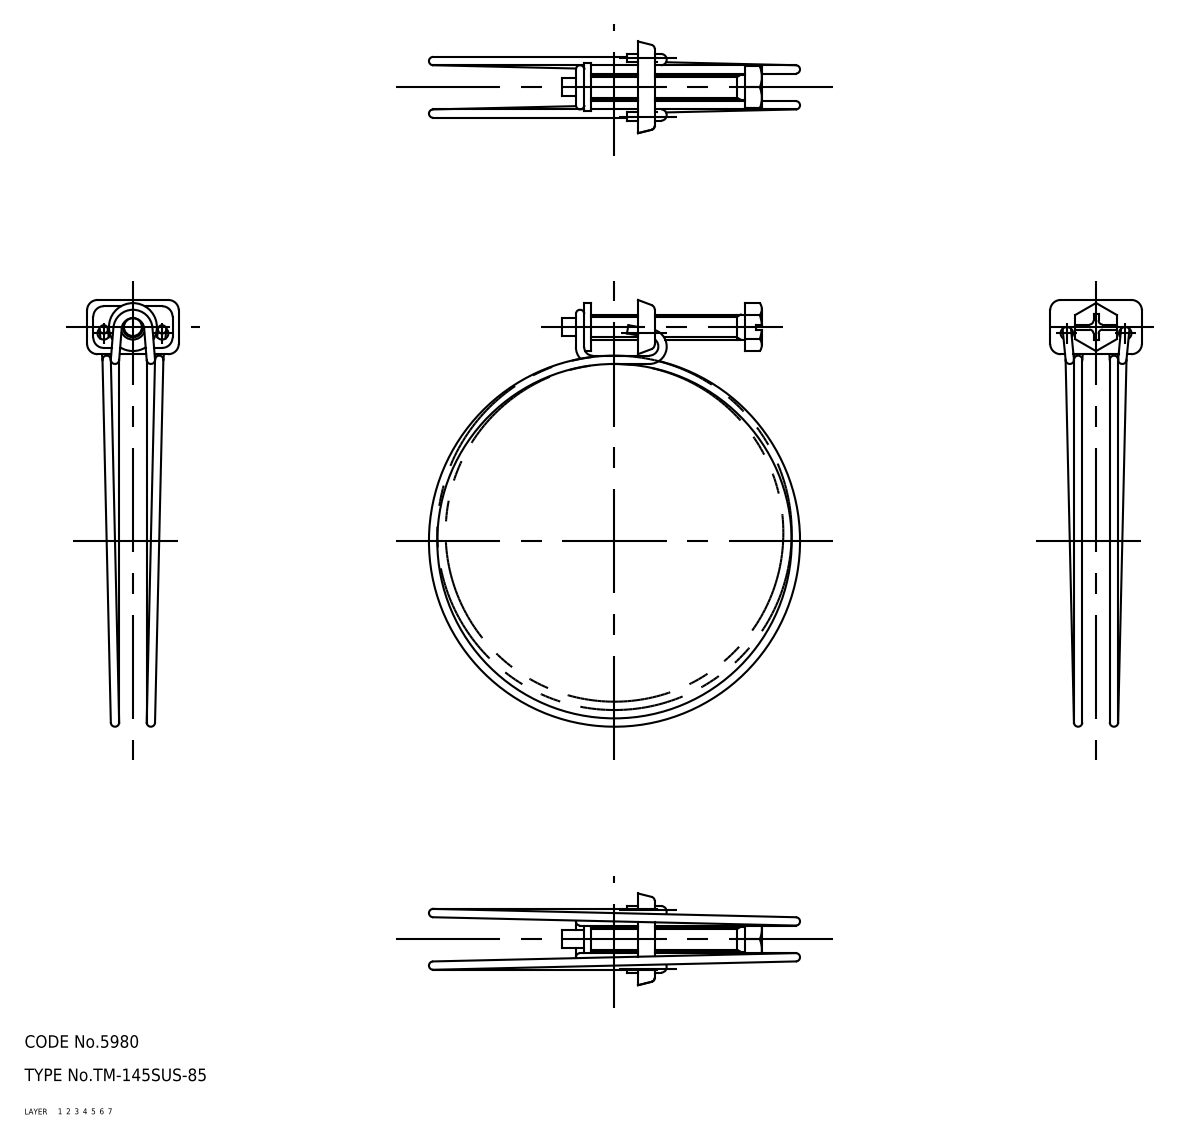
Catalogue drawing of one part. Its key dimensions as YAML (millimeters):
part_name: "screw; holder; band; TM_145SUS_85_22947_36"
step_written_by: "CADfix (AUTOMOTIVE_DESIGN)"
units: millimeters
bodies: {solids: 3, faces: 119, planar: 0, cylindrical: 0, other: 119}
overall_size: [102.35, 89, 22]
volume: 4097
surface_area: 6127
